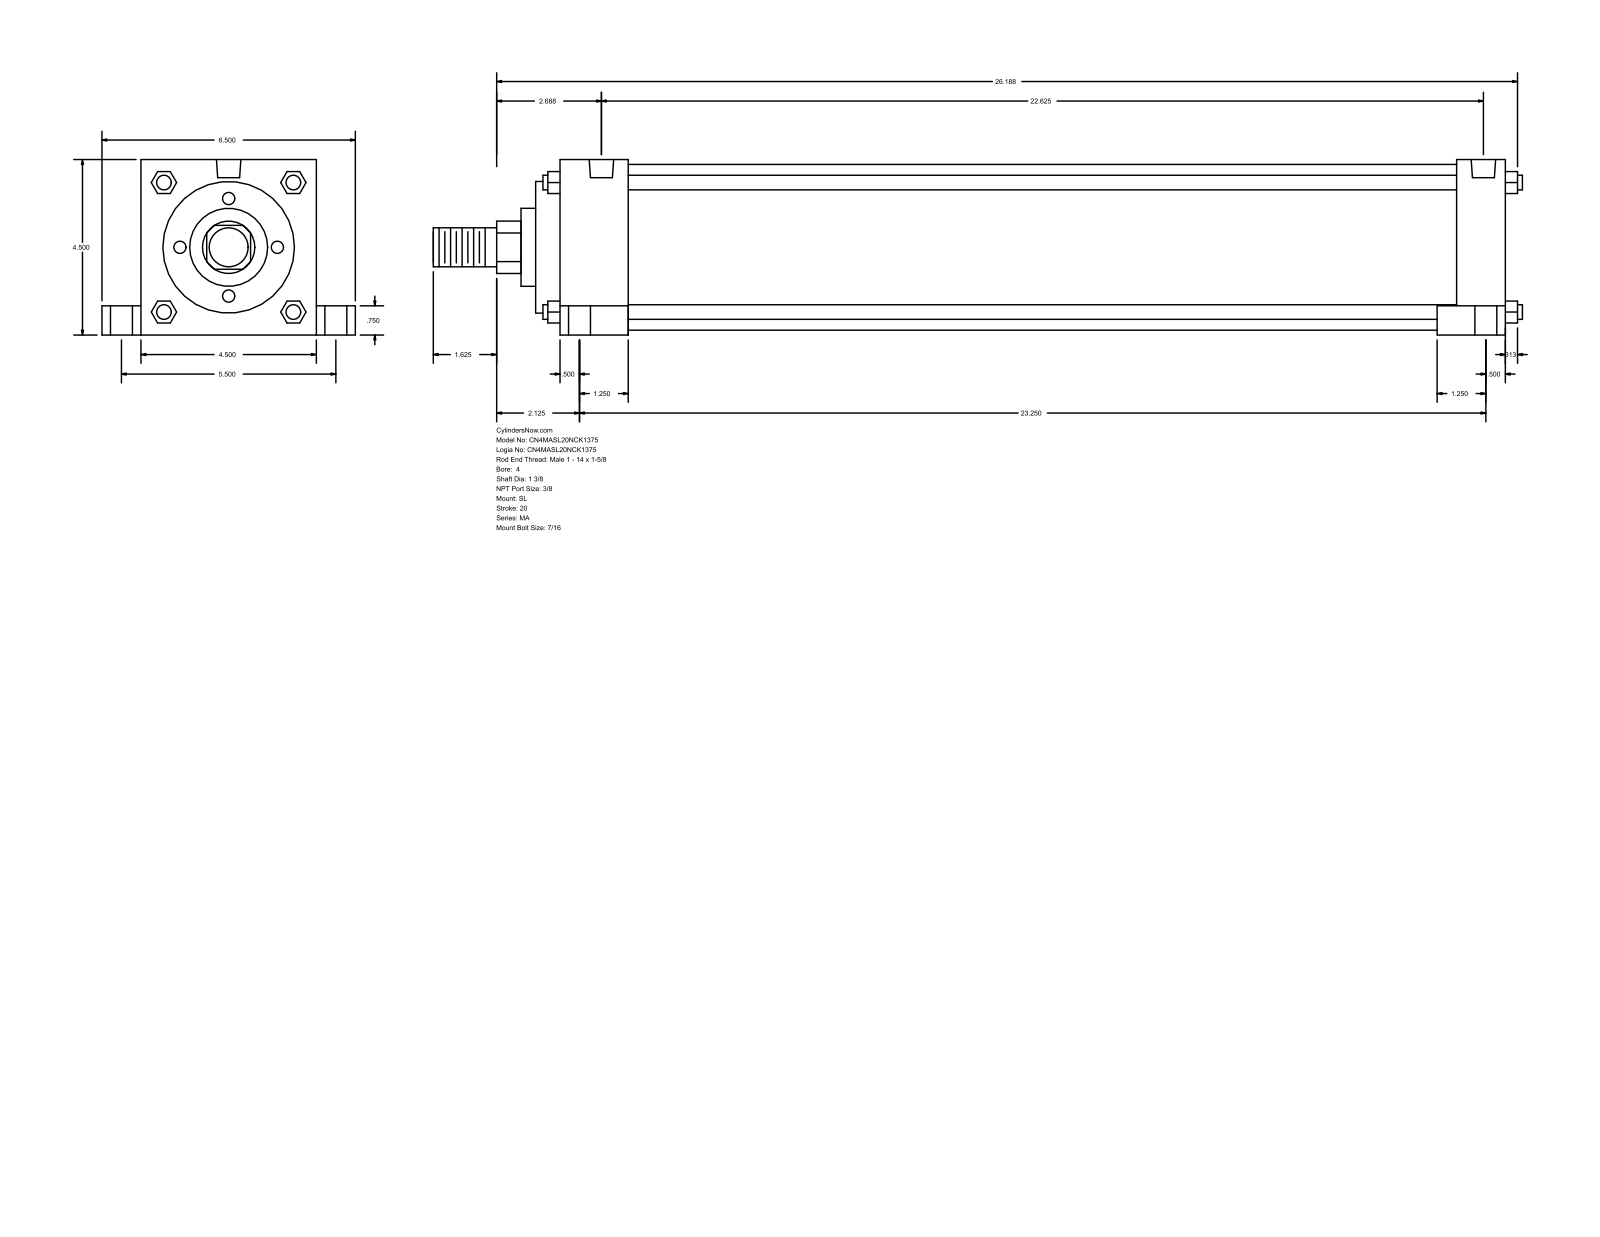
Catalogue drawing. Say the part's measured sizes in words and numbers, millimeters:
The part is named "MA_SL__0400_1.375". Its 3-D file was written by "GSSL Pune (CONFIG_CONTROL_DESIGN)". It is 0 solids with 150 faces: 113 planar, 37 cylindrical and 0 other. Overall it measures 709.61 by 165.1 by 114.3 millimeters. Round holes: 4 of diameter 11.11, 4 of diameter 14.29, 4 of diameter 20.64, 2 of diameter 15.93. Round bosses or shafts: 4 of diameter 9.53, 1 of diameter 107.95, 1 of diameter 85.72, 1 of diameter 50.8, 1 of diameter 34.92, 1 of diameter 25.4. Partial cylindrical surfaces (rounded edges, fillets, slot ends): 1 of radius 17.06. The main face-to-face distances are 114.3, 615.96, 15.87, 631.83, 60.32, 44.45, 571.51, 600.08, 584.21, 539.76. The hole center spacings are 4.77, 69.87, 70.14, 71.29, 72.4, 139.7, 565.14, 569.91.
